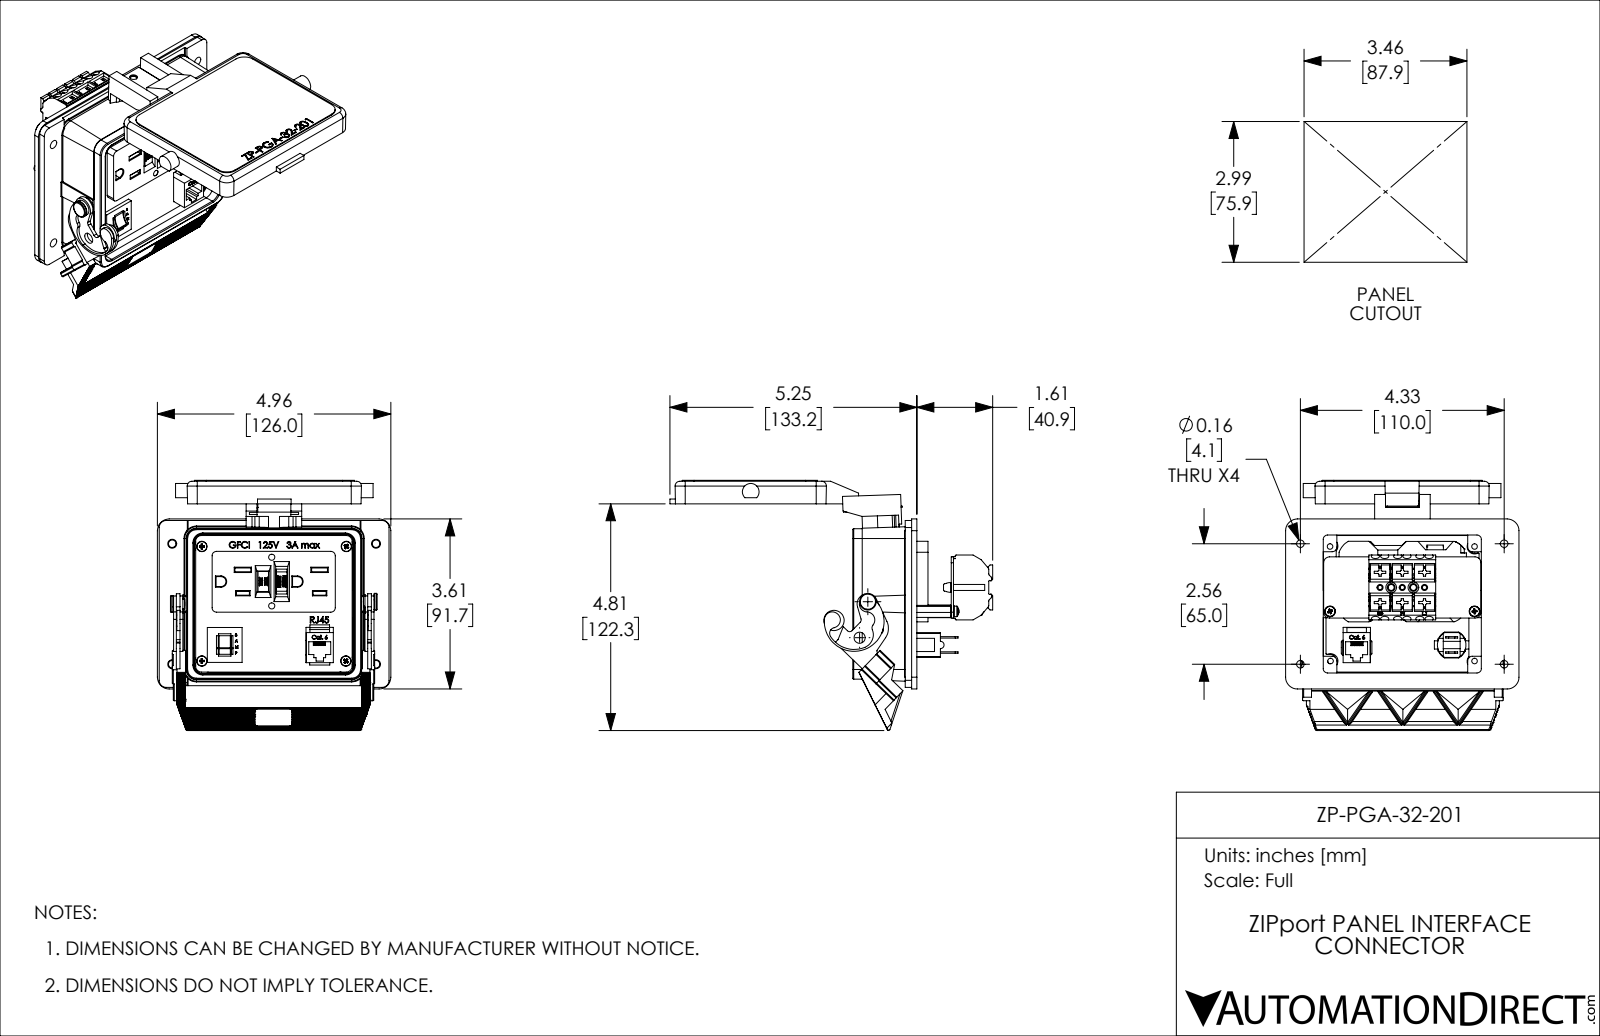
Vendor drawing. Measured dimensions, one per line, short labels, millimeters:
name: ZP-PGA-32-201
written by: SolidWorks 2017 (AUTOMOTIVE_DESIGN)
unit: mm
bodies: 1 solid, 3229 faces (2220 planar, 612 cylindrical, 397 other)
size: 174.2 × 135 × 126
volume: 269 400 mm³; area: 125 700 mm²
holes: 8× ⌀3.7, 6× ⌀3.5, 6× ⌀4.4, 4× ⌀2.5, 4× ⌀3.3, 4× ⌀4.1, 4× ⌀4.4, 4× ⌀4.8, 3× ⌀2.3, 2× ⌀2.5, 2× ⌀3, 2× ⌀3.2
bosses: 6× ⌀5.6, 6× ⌀3, 4× ⌀8, 3× ⌀5.2, 2× ⌀9, 2× ⌀5.7, 2× ⌀2.4, 1× ⌀10.9
rounds: 26× R0.5, 18× R2.5, 14× R3.2, 13× R0.4, 12× R0.6, 12× R6.4, 8× R2.4, 8× R3.8
face distances: 3.4, 1.5, 25.8, 24.3, 18.5, 42.8, 44.3, 12.5, 6, 30.2
hole spacings: 12, 27, 35, 78, 6, 16.1, 32.7, 39.9
